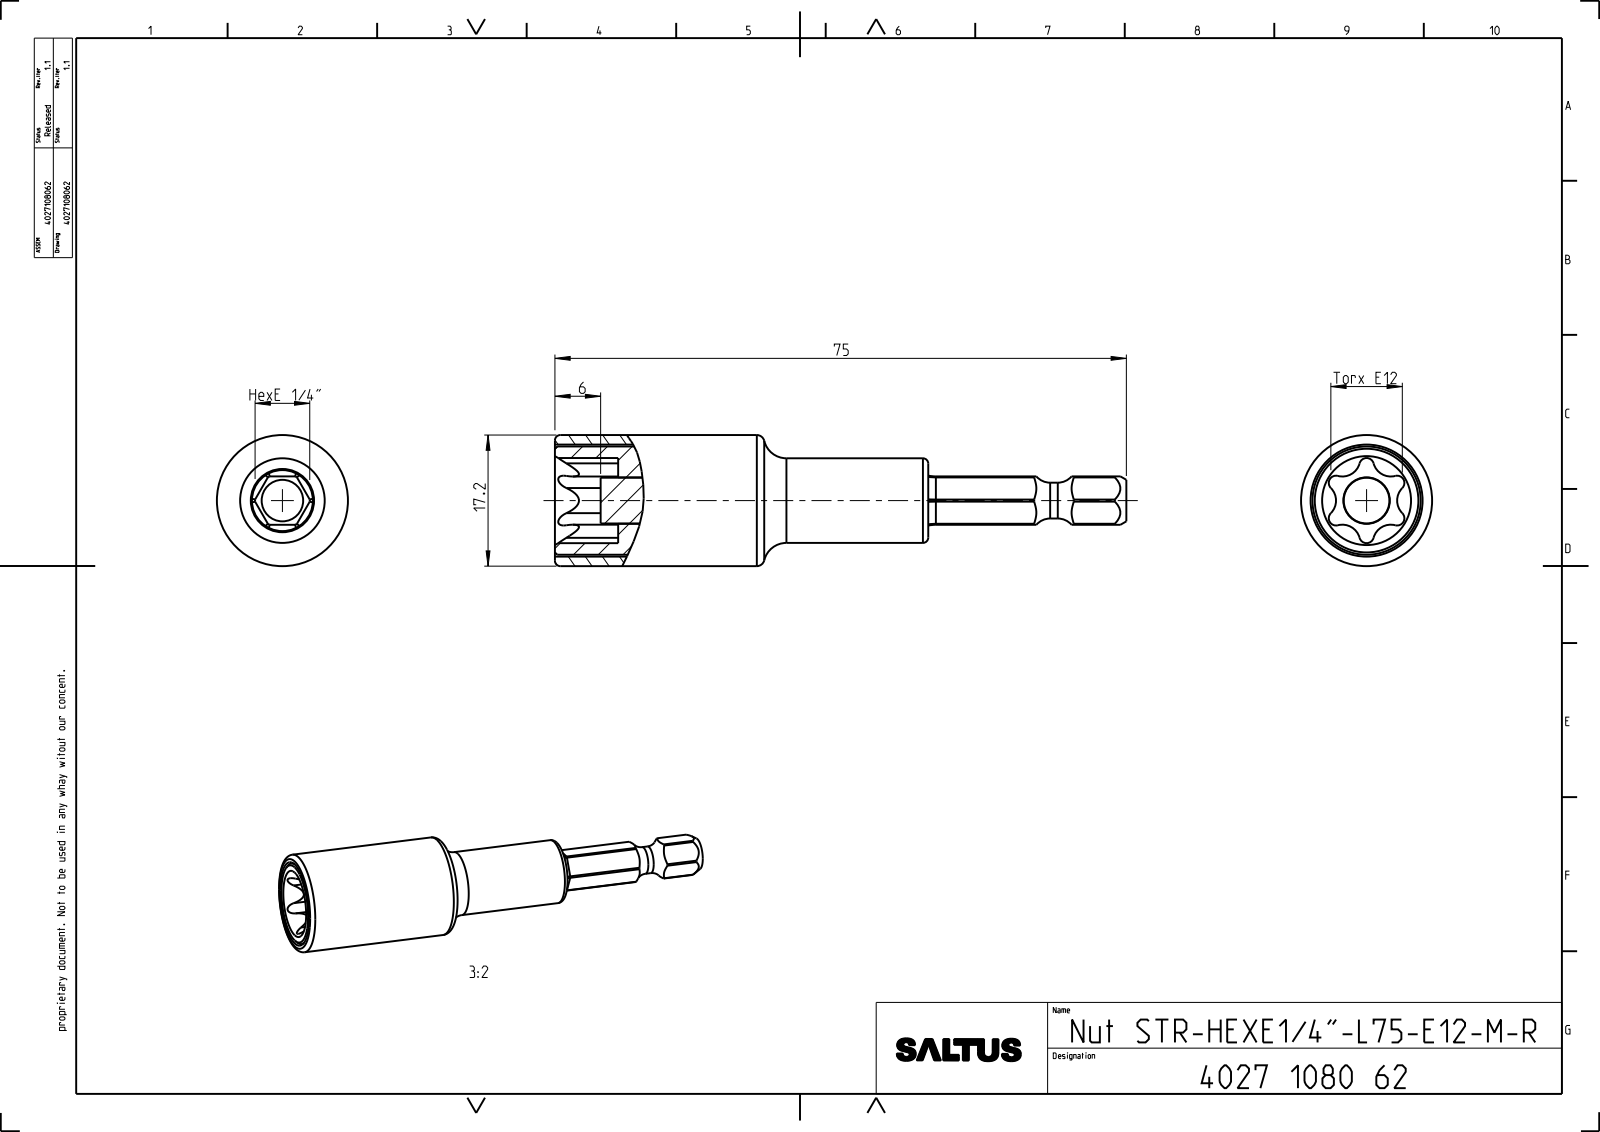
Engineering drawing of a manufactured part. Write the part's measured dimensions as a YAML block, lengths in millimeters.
part_name: "4027911279; 4027040603; 4027108062_ASM"
step_written_by: "CREO PARAMETRIC BY PTC INC, 2022414 (CONFIG_CONTROL_DESIGN)"
units: millimeters
bodies: {solids: 3, faces: 108, planar: 20, cylindrical: 52, other: 36}
overall_size: [75, 17.2, 17.2]
volume: 7958
surface_area: 7332
round_holes:
  - {diameter: 6.1, count: 1}
  - {diameter: 8.3, count: 1}
  - {diameter: 14.7, count: 1}
round_bosses_or_shafts:
  - {diameter: 17.2, count: 1}
  - {diameter: 14.2, count: 1}
  - {diameter: 11.1, count: 1}
  - {diameter: 8, count: 1}
  - {diameter: 6, count: 1}
  - {diameter: 4.7, count: 1}
partial_cylinders:
  - {radius: 0.95, count: 6}
  - {radius: 2.34, count: 6}
  - {radius: 5, count: 6}
  - {radius: 3.59, count: 1}
face_to_face_distances: [6.34, 6.36, 25.5, 17.2, 8.3, 10.5, 19.5, 6.7, 9, 15]
